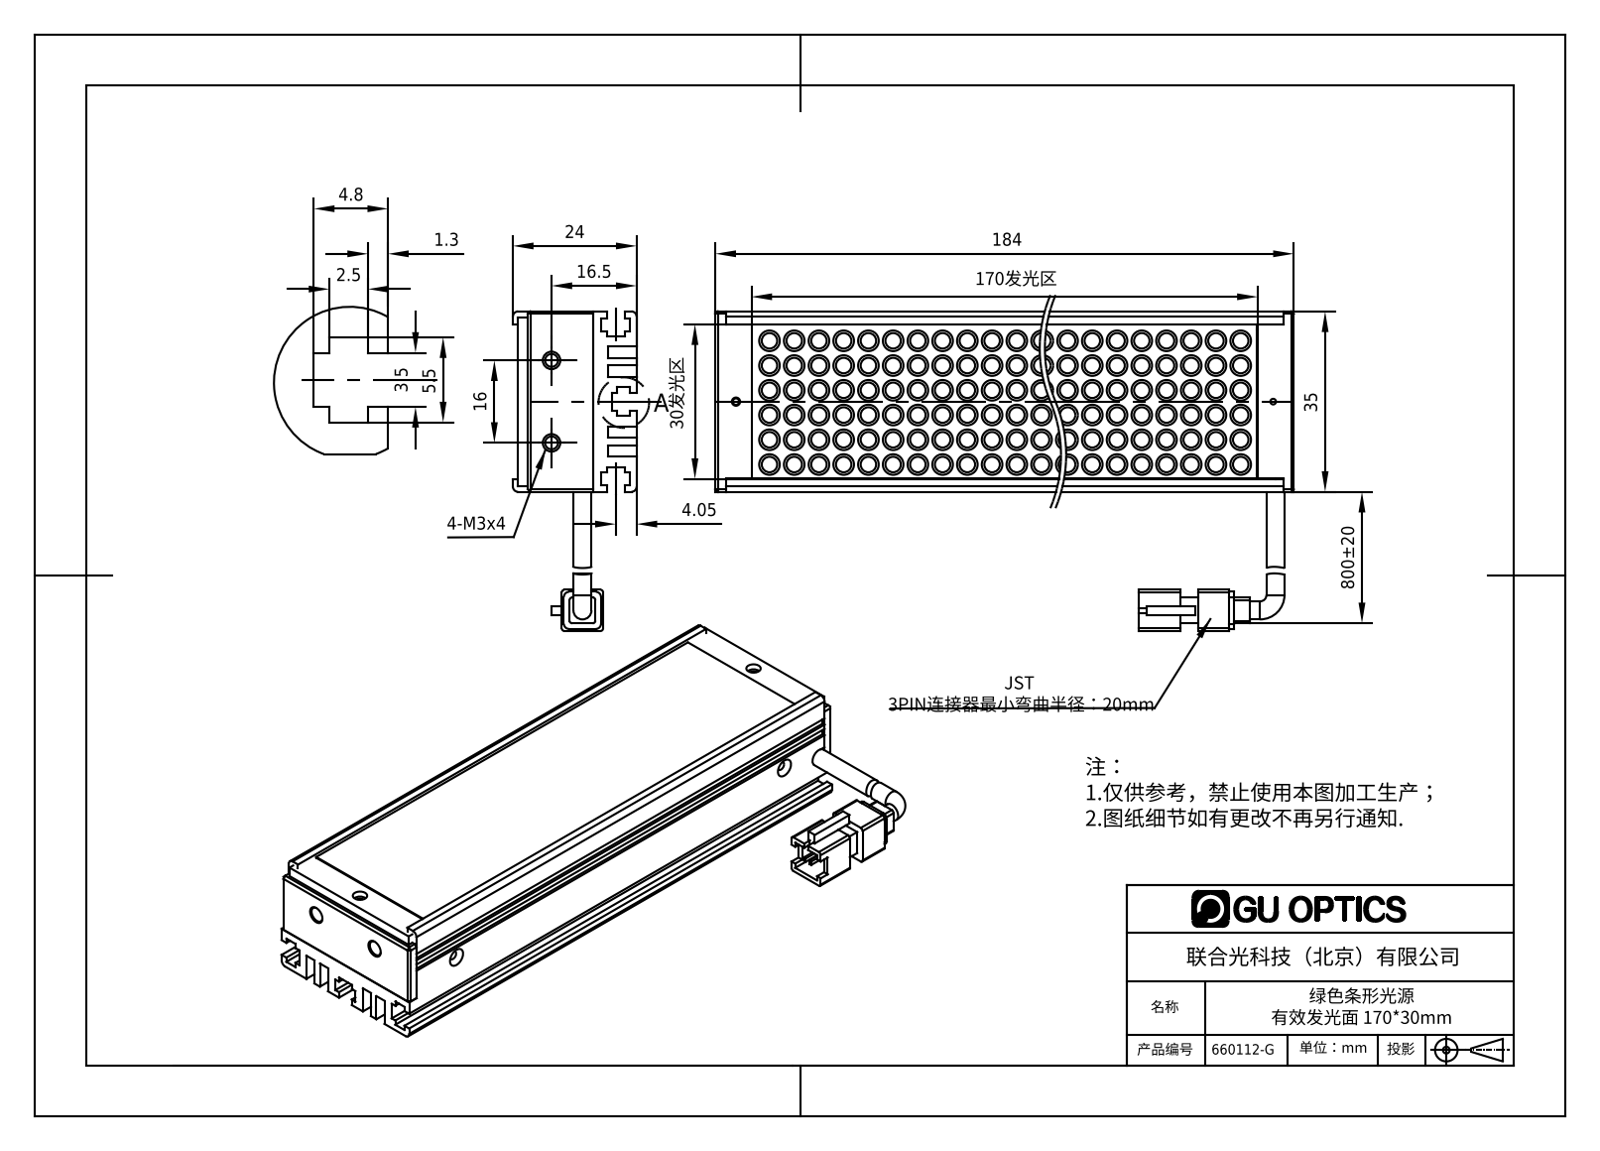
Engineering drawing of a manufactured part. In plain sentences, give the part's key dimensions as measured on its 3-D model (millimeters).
The part is named "660112-G". Its 3-D file was written by "SolidWorks 2016 (AUTOMOTIVE_DESIGN)". It is 8 solids with 1721 faces: 477 planar, 927 cylindrical and 317 other. Overall it measures 184 by 62 by 24 millimeters. Its volume is 82 743 cubic millimeters and its surface area 93 944 square millimeters. Round holes: 5 of diameter 1.6, 3 of diameter 1.7, 2 of diameter 1.5, 2 of diameter 2.5, 2 of diameter 2.8, 2 of diameter 3, 1 of diameter 1.1, 1 of diameter 1.25, 1 of diameter 2. Round bosses or shafts: 210 of diameter 4, 210 of diameter 3, 2 of diameter 3.5. Partial cylindrical surfaces (rounded edges, fillets, slot ends): 12 of radius 1, 8 of radius 0.5, 1 of radius 1.65. The main face-to-face distances are 2, 2.2, 8.6, 1, 2.5, 12.6, 14.6, 9, 4, 10.6. The hole center spacings are 176, 7, 28.05, 28.52, 60, 88.01, 88.17, 148.01.
